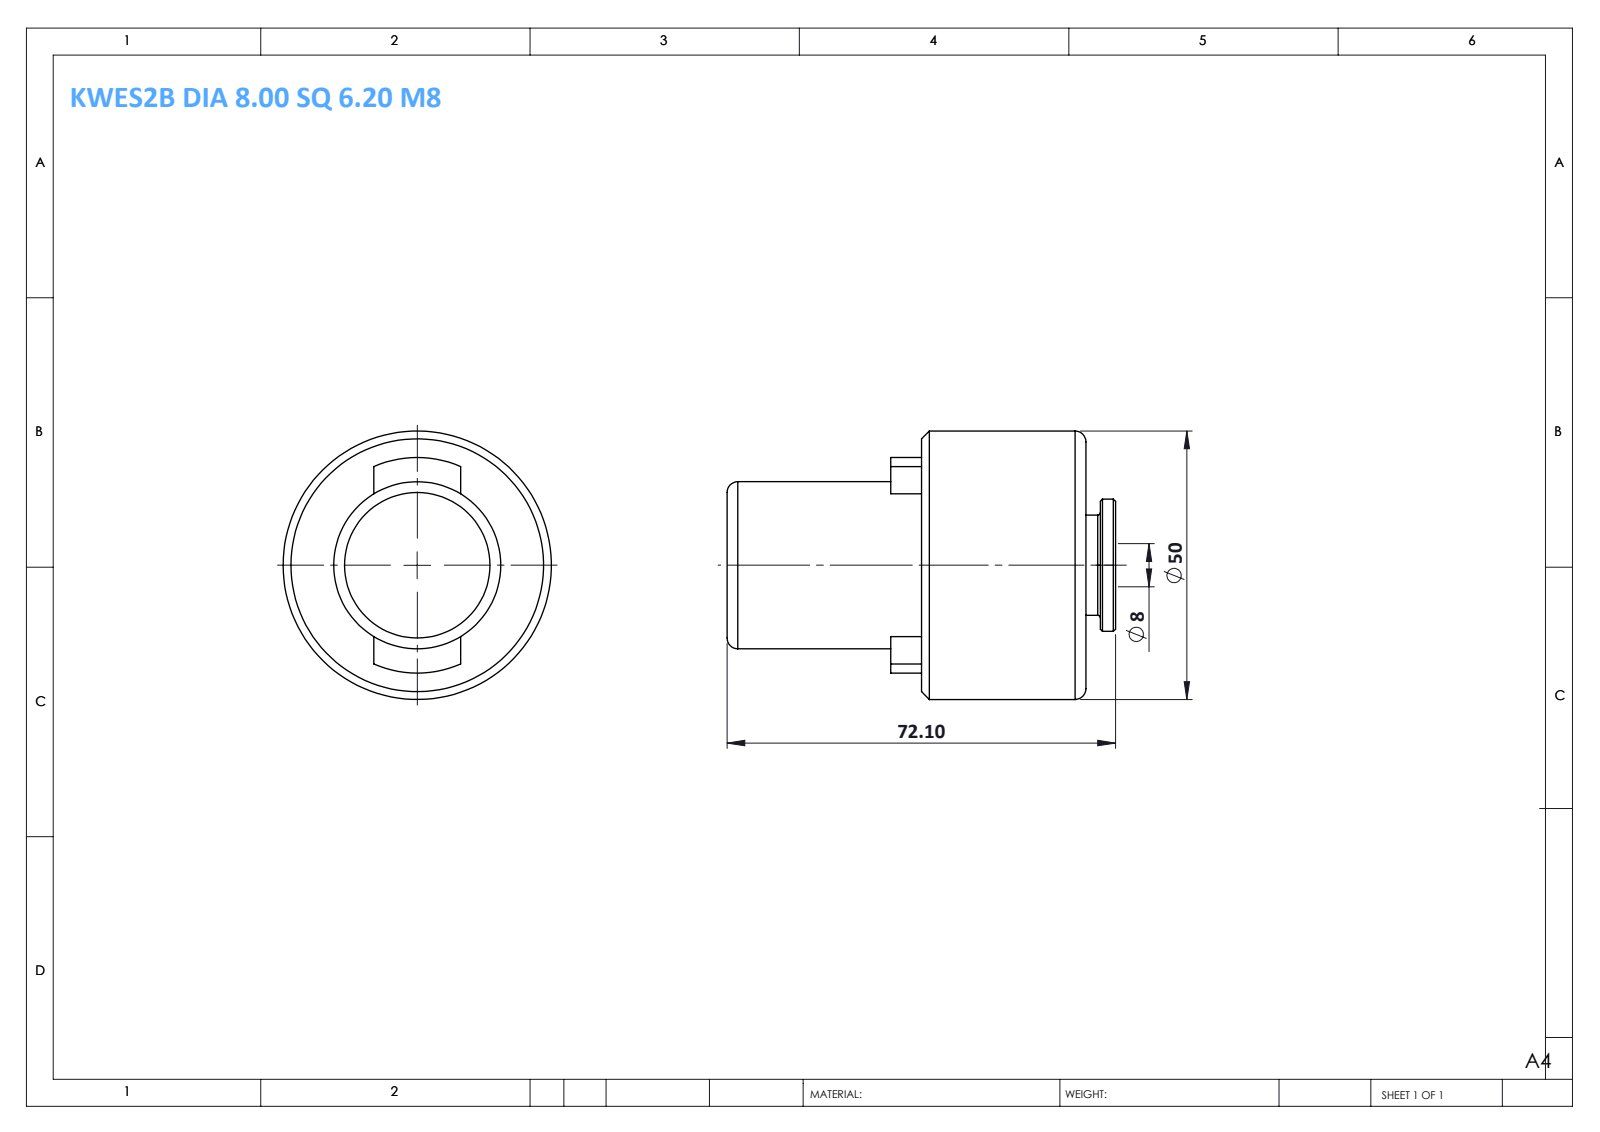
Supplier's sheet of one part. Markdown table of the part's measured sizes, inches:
| quantity | value |
| --- | --- |
| part name | KWES2B DIA 8.00 SQ 6.20 1-8'''''''' (BSPT) |
| STEP written by | SolidWorks 2014 (CONFIG_CONTROL_DESIGN) |
| units | inches |
| bodies | 1 solid, 38 faces (12 planar, 12 cylindrical, 14 other) |
| overall size | 2.839 × 1.961 × 1.961 |
| volume | 5.359 in³ |
| surface area | 20.67 in² |
| round holes (diameter × count) | 0.315 × 1 |
| round bosses / shafts (diameter × count) | 1.961 × 1, 1.22 × 1, 0.965 × 1, 0.732 × 1 |
| partial cylindrical surfaces (radius × count) | 0.787 × 1 |
| main face-to-face distances | 1.201, 1.421, 2.622, 2.839, 1.417, 0.217, 1.197, 0.224, 1.425, 1.642 |
